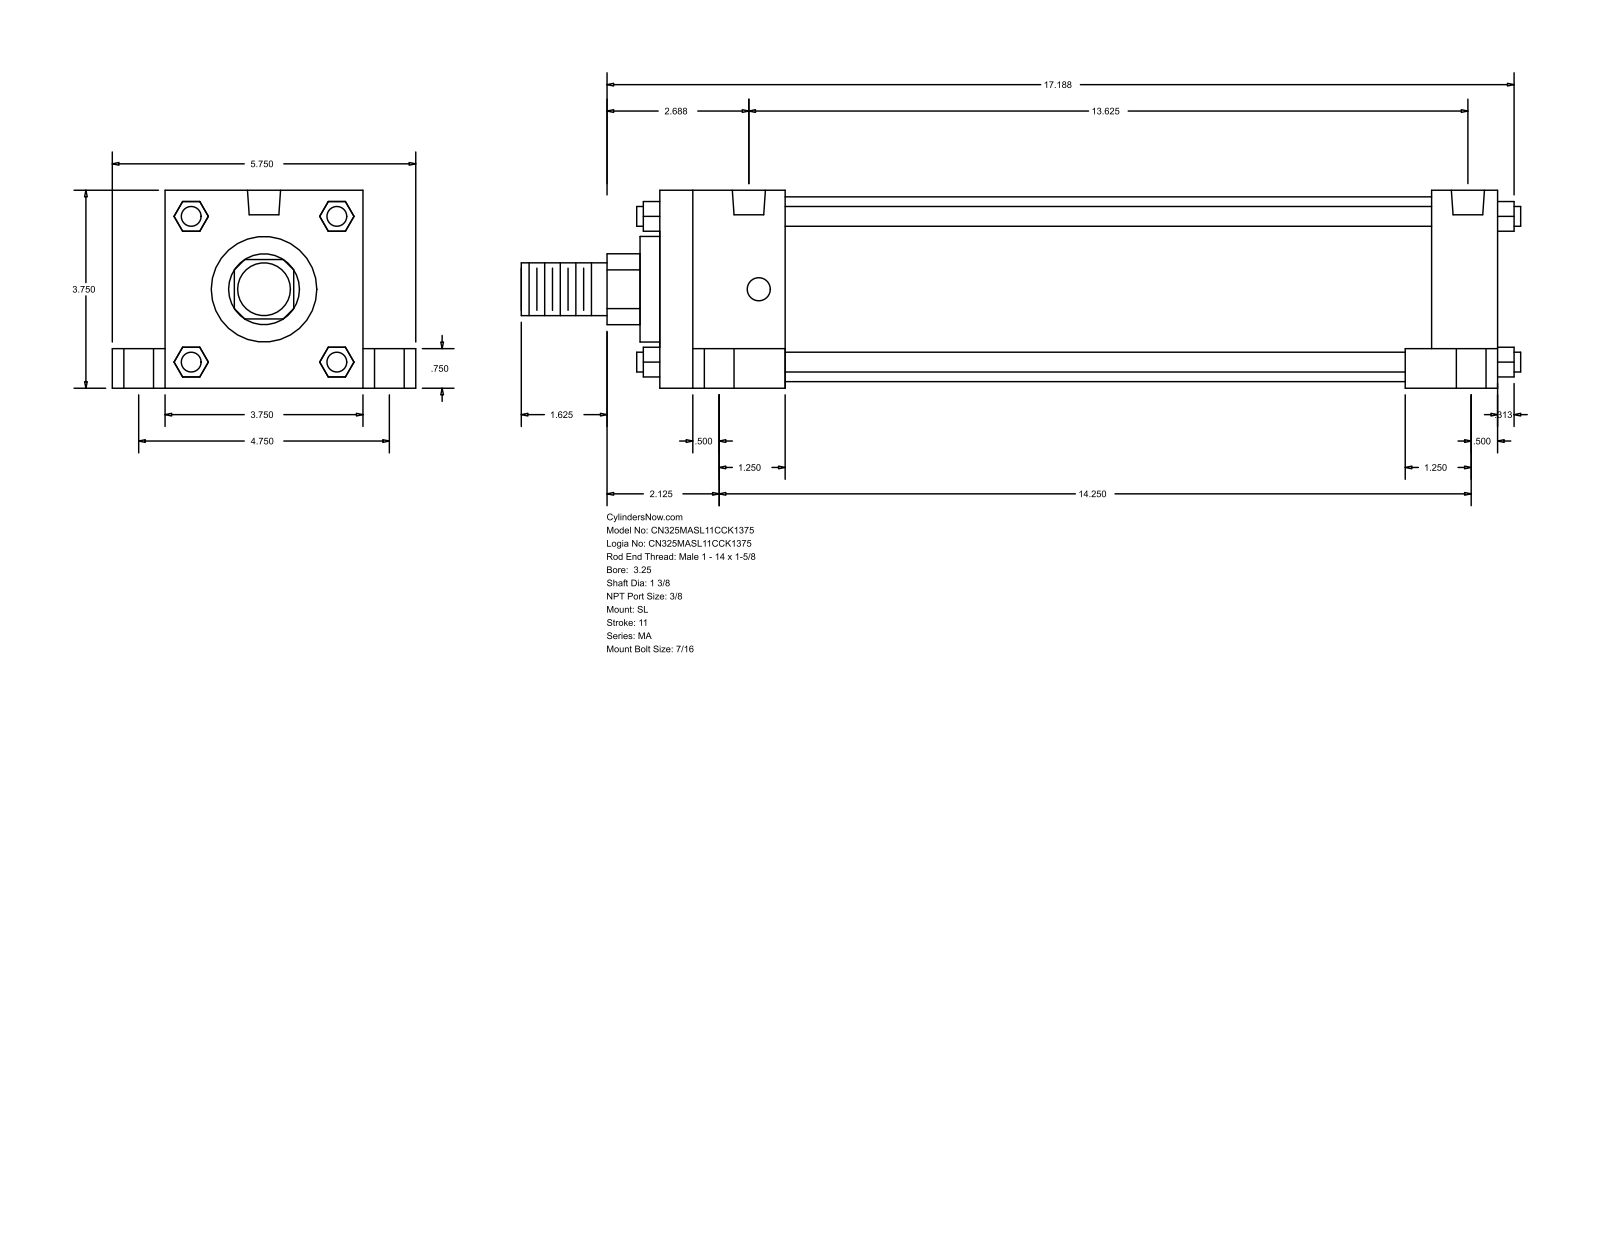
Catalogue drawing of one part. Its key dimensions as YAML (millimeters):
part_name: "MA_SL__0325_1.375"
step_written_by: "GSSL Pune (CONFIG_CONTROL_DESIGN)"
units: millimeters
bodies: {solids: 0, faces: 148, planar: 112, cylindrical: 36, other: 0}
overall_size: [481.01, 146.05, 95.25]
round_holes:
  - {diameter: 11.11, count: 4}
  - {diameter: 14.29, count: 4}
  - {diameter: 20.64, count: 4}
  - {diameter: 15.93, count: 2}
round_bosses_or_shafts:
  - {diameter: 9.53, count: 4}
  - {diameter: 88.9, count: 1}
  - {diameter: 50.8, count: 1}
  - {diameter: 34.92, count: 1}
  - {diameter: 25.4, count: 1}
partial_cylinders:
  - {radius: 17.06, count: 1}
face_to_face_distances: [95.24, 403.22, 25.41, 120.65, 371.48, 31.74, 60.32, 311.16, 342.9, 19.05]
hole_center_spacings: [4.77, 60.35, 60.66, 62, 63.27, 120.66, 336.54, 341.31]
